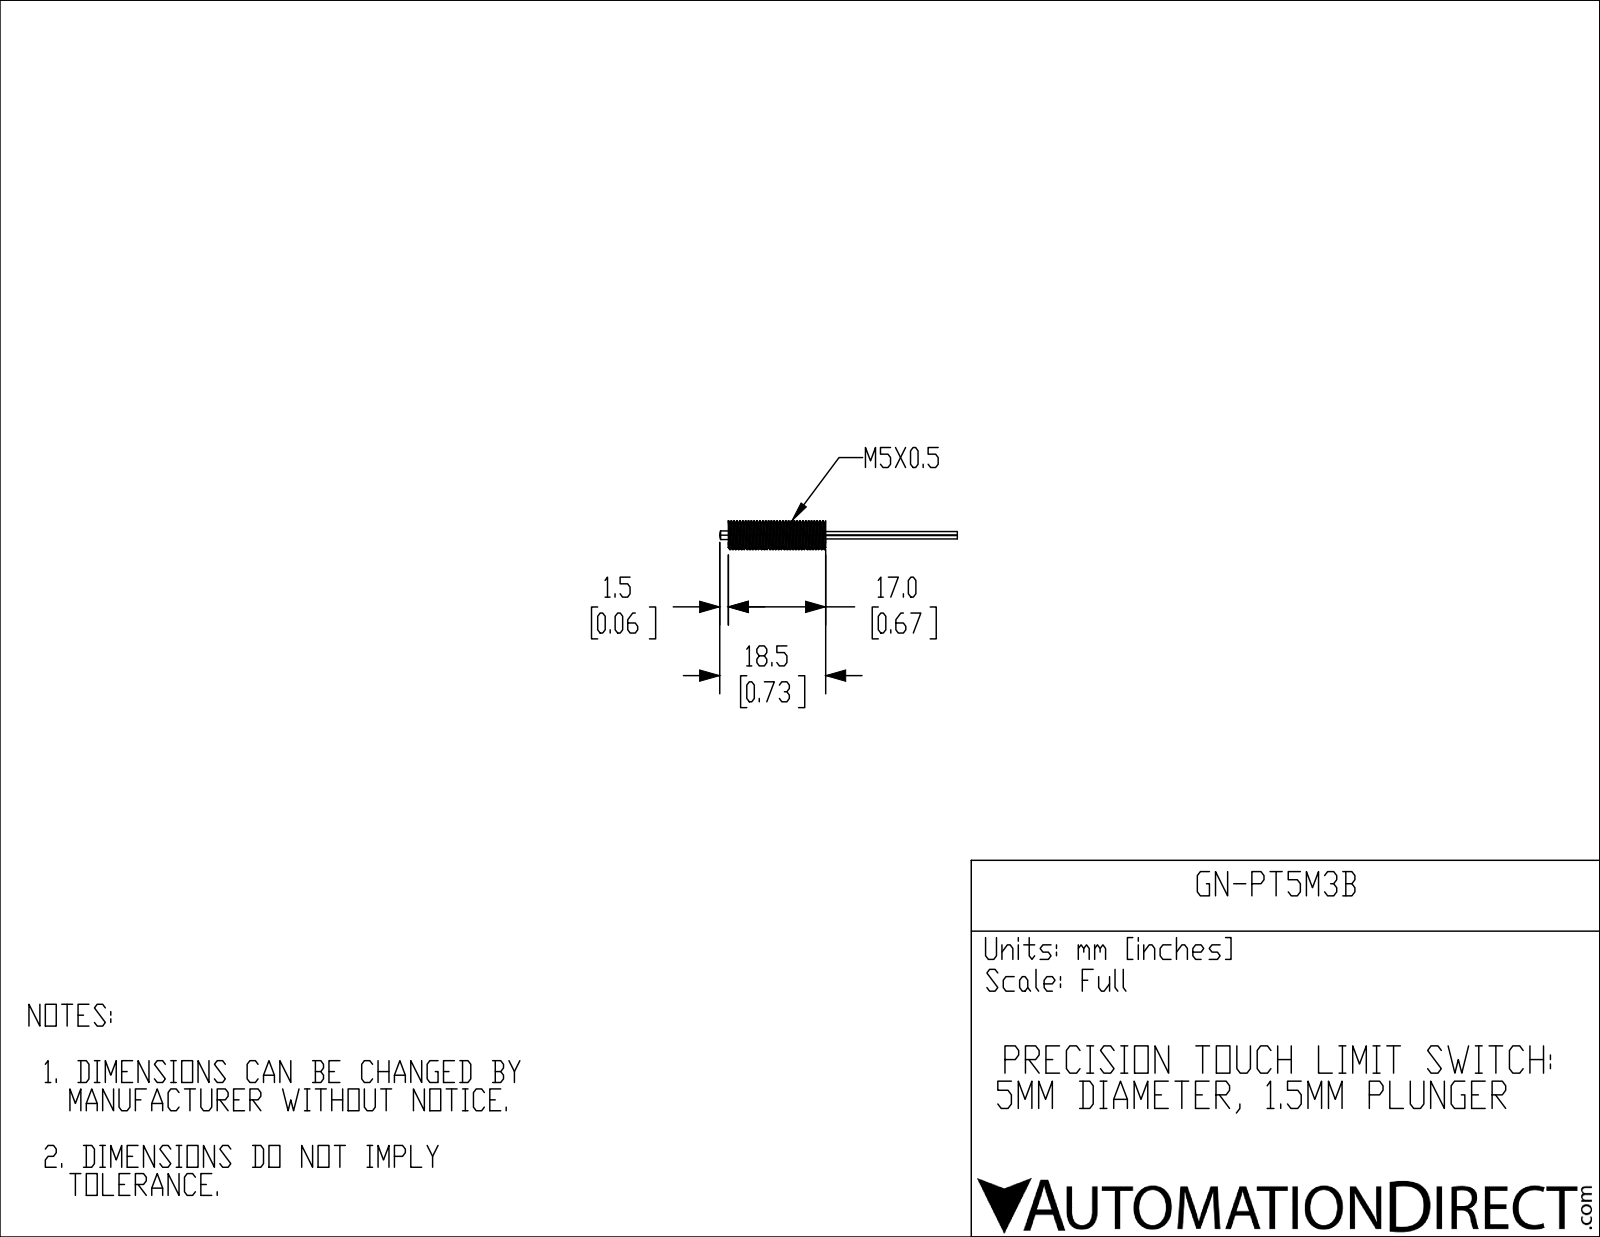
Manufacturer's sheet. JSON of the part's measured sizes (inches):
{"part_name": "GN-PT5M3B", "step_written_by": "SolidWorks 2018 (AUTOMOTIVE_DESIGN)", "units": "inches", "bodies": {"solids": 1, "faces": 11, "planar": 4, "cylindrical": 4, "other": 3}, "overall_size": [1.634, 0.197, 0.197], "volume_in3": 0.021, "surface_area_in2": 0.614, "round_bosses_or_shafts": [[0.024, 2], [0.197, 1], [0.059, 1]], "face_to_face_distances": [0.669, 1.575, 0.906]}
